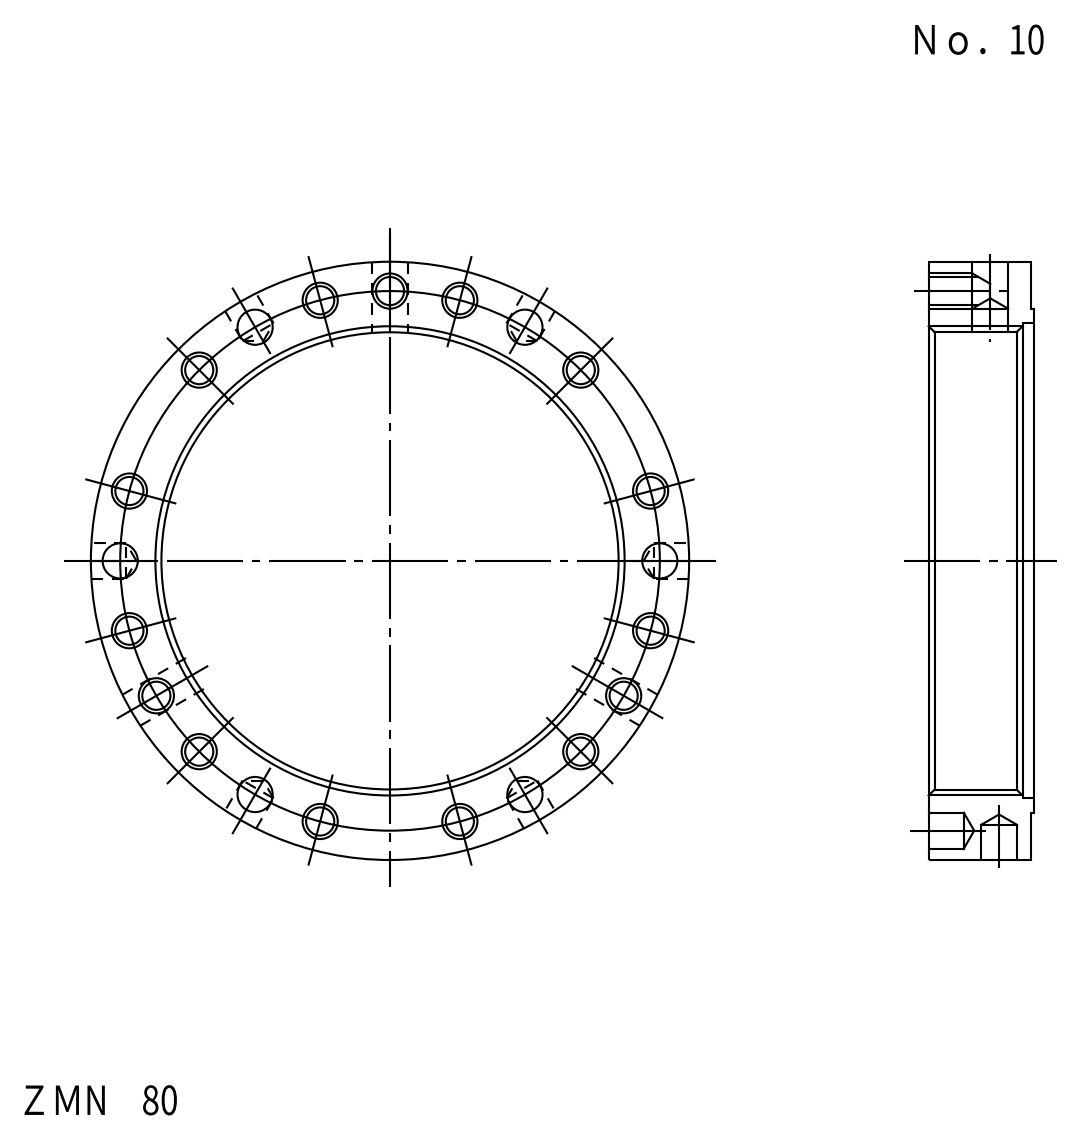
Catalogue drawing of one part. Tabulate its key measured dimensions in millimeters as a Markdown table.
| quantity | value |
| --- | --- |
| part name | FKD ZMN80 |
| STEP written by | Autodesk Inventor LT (CONFIG_CONTROL_DESIGN) |
| units | millimeters |
| bodies | 1 solid, 62 faces (4 planar, 34 cylindrical, 24 other) |
| overall size | 102 × 102 × 18 |
| volume | 48 898 mm³ |
| surface area | 20 781 mm² |
| round holes (diameter × count) | 4.92 × 14, 6.1 × 12, 4.92 × 1, 80 × 1, 81 × 1 |
| round bosses / shafts (diameter × count) | 102 × 1, 86 × 1 |
| main face-to-face distances | 17.5, 0.5, 18, 1.5, 1, 16.5 |
| hole center spacings | 46, 72.99, 85, 88.87, 79.68, 12.01, 23.81, 35.21 |
